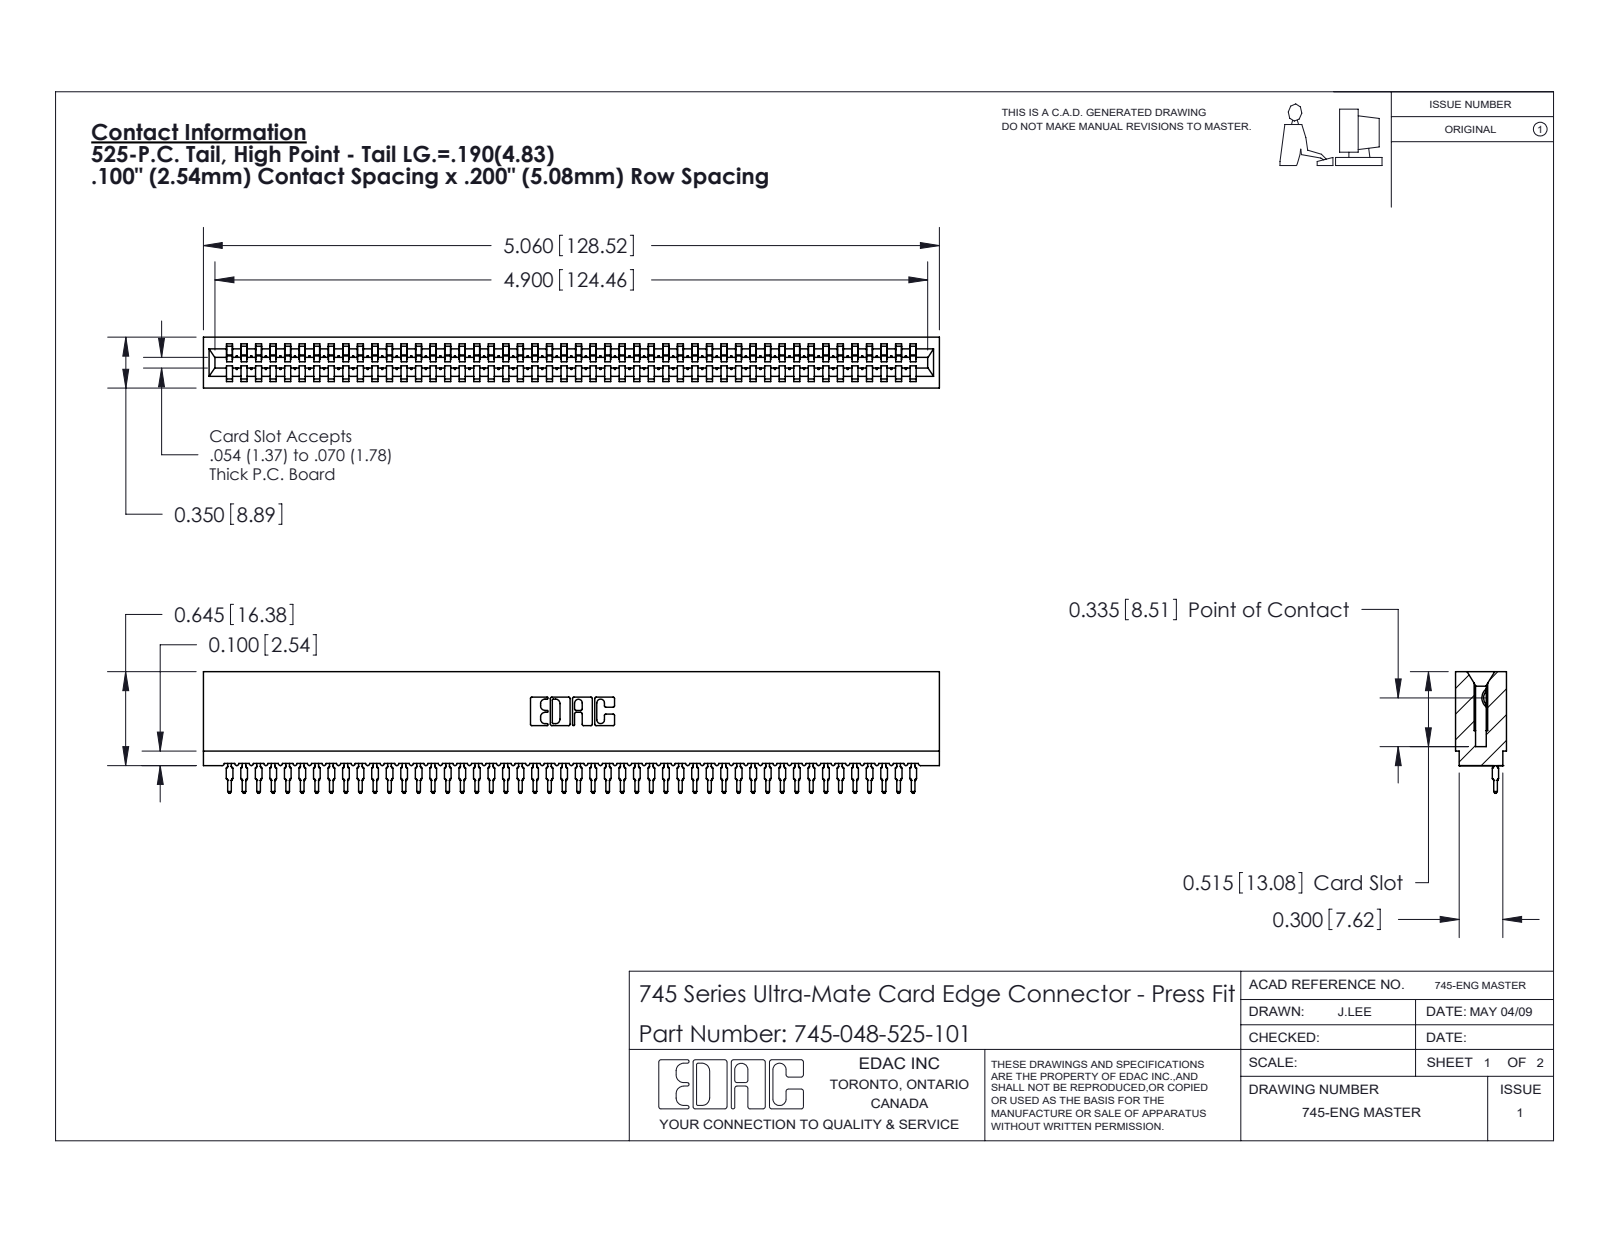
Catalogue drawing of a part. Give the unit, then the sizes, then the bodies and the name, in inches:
Units: inches
Overall size (bounding box): 5.06 × 0.836 × 0.35
Partial cylindrical surfaces — rounded edges, fillets, slot ends (radius × count): R0.015 ×96, R0.021 ×96, R0.01 ×22, R0.007 ×6, R0.031 ×6, R0.005 ×4, R0.011 ×4, R0.026 ×3
Main face-to-face distances: 0.35, 0.045, 0.305, 0.138, 0.212, 0.093, 0.167, 0.063, 0.287, 0.243
Volume: 0.675 in³ · Surface area: 31.96 in²
Bodies: 49 solids, 5471 faces (3271 planar, 952 cylindrical, 1248 other)
Part name (STEP PRODUCT): 745-292-001_525; 745-048-525-101; 745 Part_Insulator Option - 01
STEP written by: SolidWorks 2020 (CONFIG_CONTROL_DESIGN)
